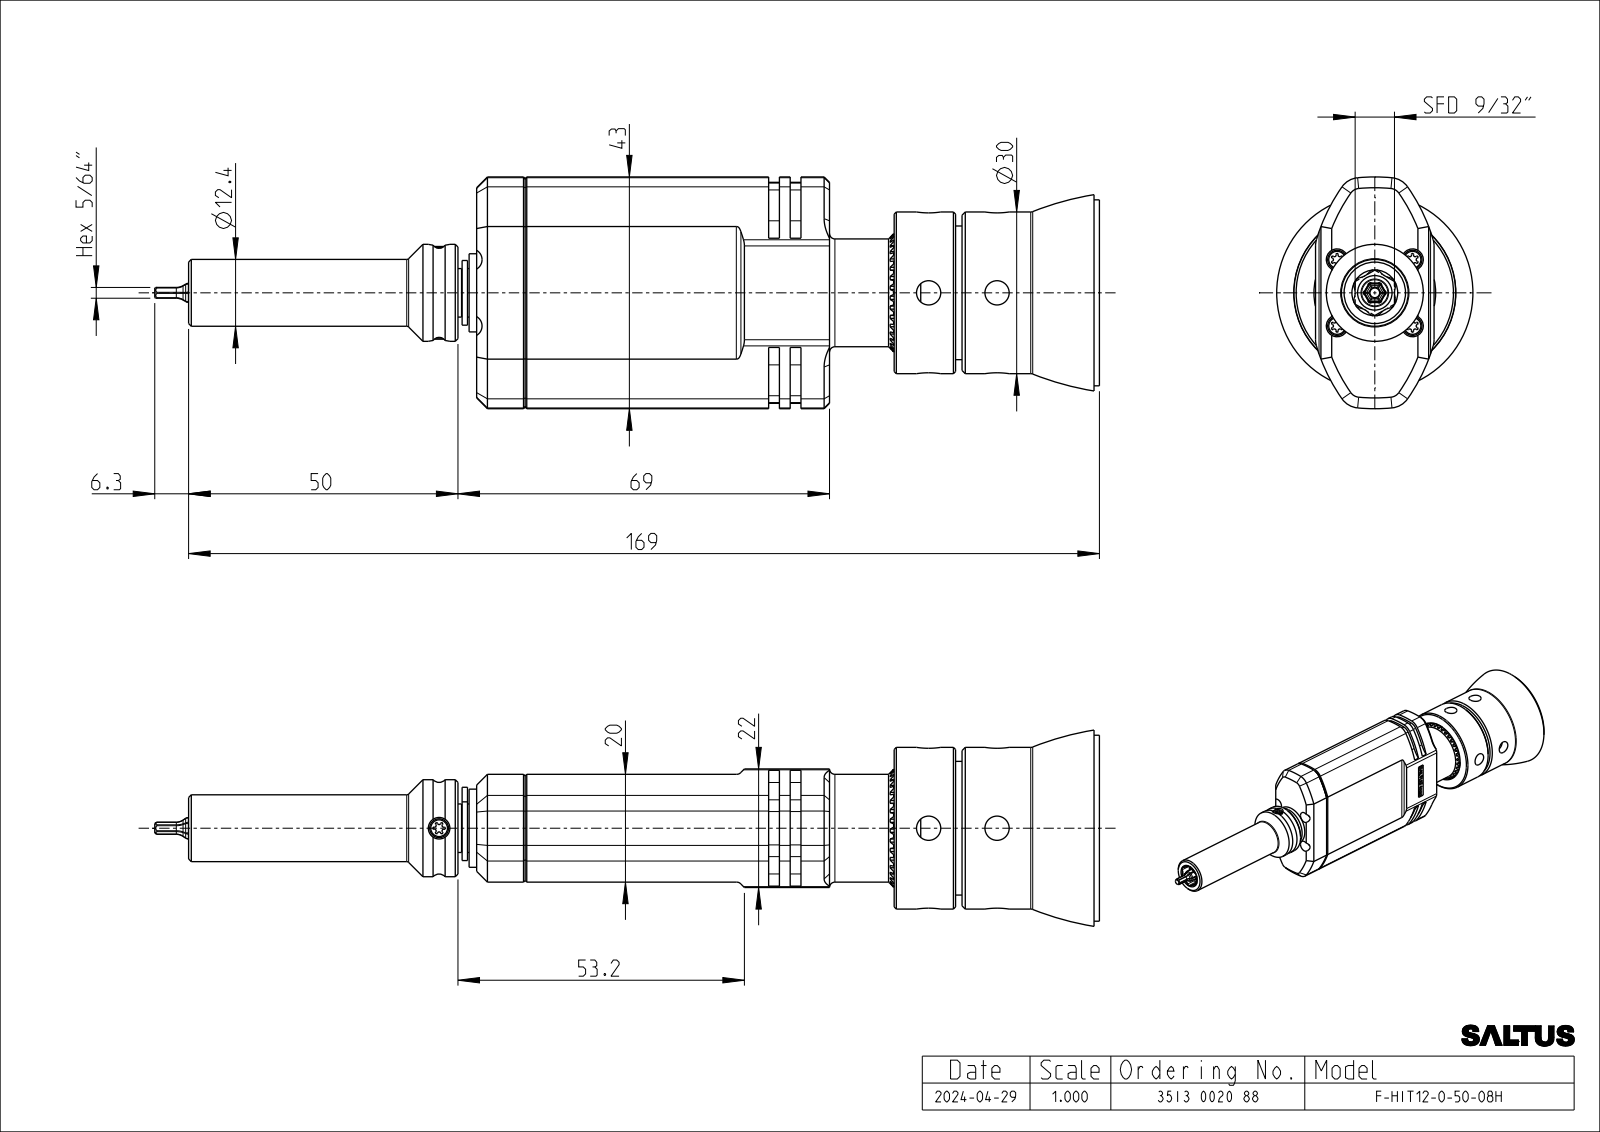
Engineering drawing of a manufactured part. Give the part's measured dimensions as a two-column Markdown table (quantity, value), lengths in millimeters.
| quantity | value |
| --- | --- |
| part name | 3513002088_SW0001 |
| STEP written by | CREO PARAMETRIC BY PTC INC, 2022414 (CONFIG_CONTROL_DESIGN) |
| units | millimeters |
| bodies | 1 solid, 797 faces (245 planar, 341 cylindrical, 211 other) |
| overall size | 175.4 × 43 × 36.4 |
| volume | 90 290 mm³ |
| surface area | 18 650 mm² |
| round holes (diameter × count) | 4 × 5, 4.5 × 4, 1.2 × 2, 9.1 × 1 |
| round bosses / shafts (diameter × count) | 3.5 × 5, 34.5 × 1, 30 × 1, 24.8 × 1, 20 × 1, 18 × 1, 14.5 × 1, 12.4 × 1 |
| partial cylindrical surfaces (radius × count) | 0.2 × 42, 0.3 × 30, 1 × 18, 3 × 10, 4 × 8, 0.8 × 6, 2.5 × 6, 33 × 6 |
| main face-to-face distances | 20, 1, 21, 50.1, 115.6, 65.5, 38.1, 12, 77.5, 22 |
| hole center spacings | 9.3, 4.5, 6.2, 8.1, 12.3, 12.7, 13.6, 14 |
